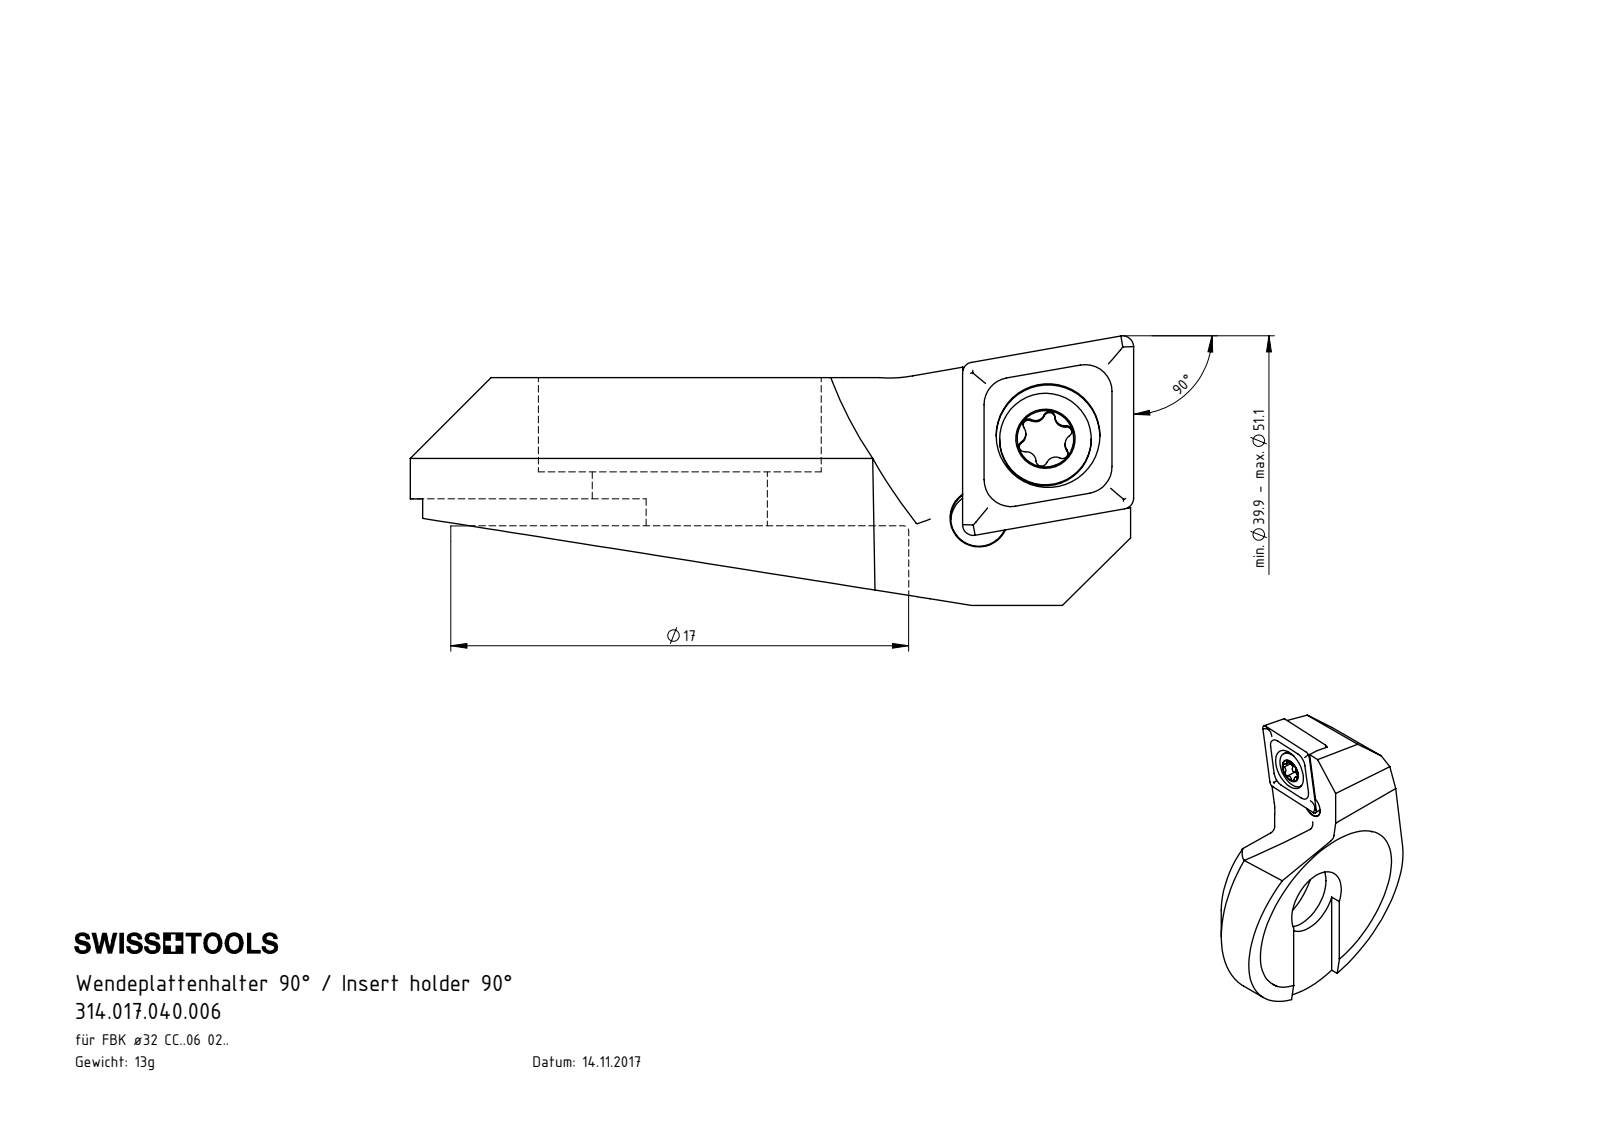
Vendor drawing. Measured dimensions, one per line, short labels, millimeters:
name: CCMT060204; F32.WCA.001.007; F32-WCA.001.007_C_fertigbearbeitet; WCA-ER2.001.006_A
written by: SolidWorks 2017 (AUTOMOTIVE_DESIGN)
unit: mm
bodies: 3 solids, 103 faces (38 planar, 26 cylindrical, 39 other)
size: 26.85 × 20 × 10
volume: 1 559 mm³; area: 1 544 mm²
holes: 1× ⌀2.05, 1× ⌀2.1, 1× ⌀2.8, 1× ⌀3.85, 1× ⌀6.5, 1× ⌀10.5
bosses: 1× ⌀3.4, 1× ⌀2.5
rounds: 6× R0.21, 5× R0.36, 2× R0.5, 1× R0.36, 1× R5, 1× R8.5, 1× R10, 1× R15
face distances: 1, 5.5, 3.5, 2, 4.5, 2.28, 8.45, 4.95, 3.95, 2.95
hole spacings: 3.84, 3.99
